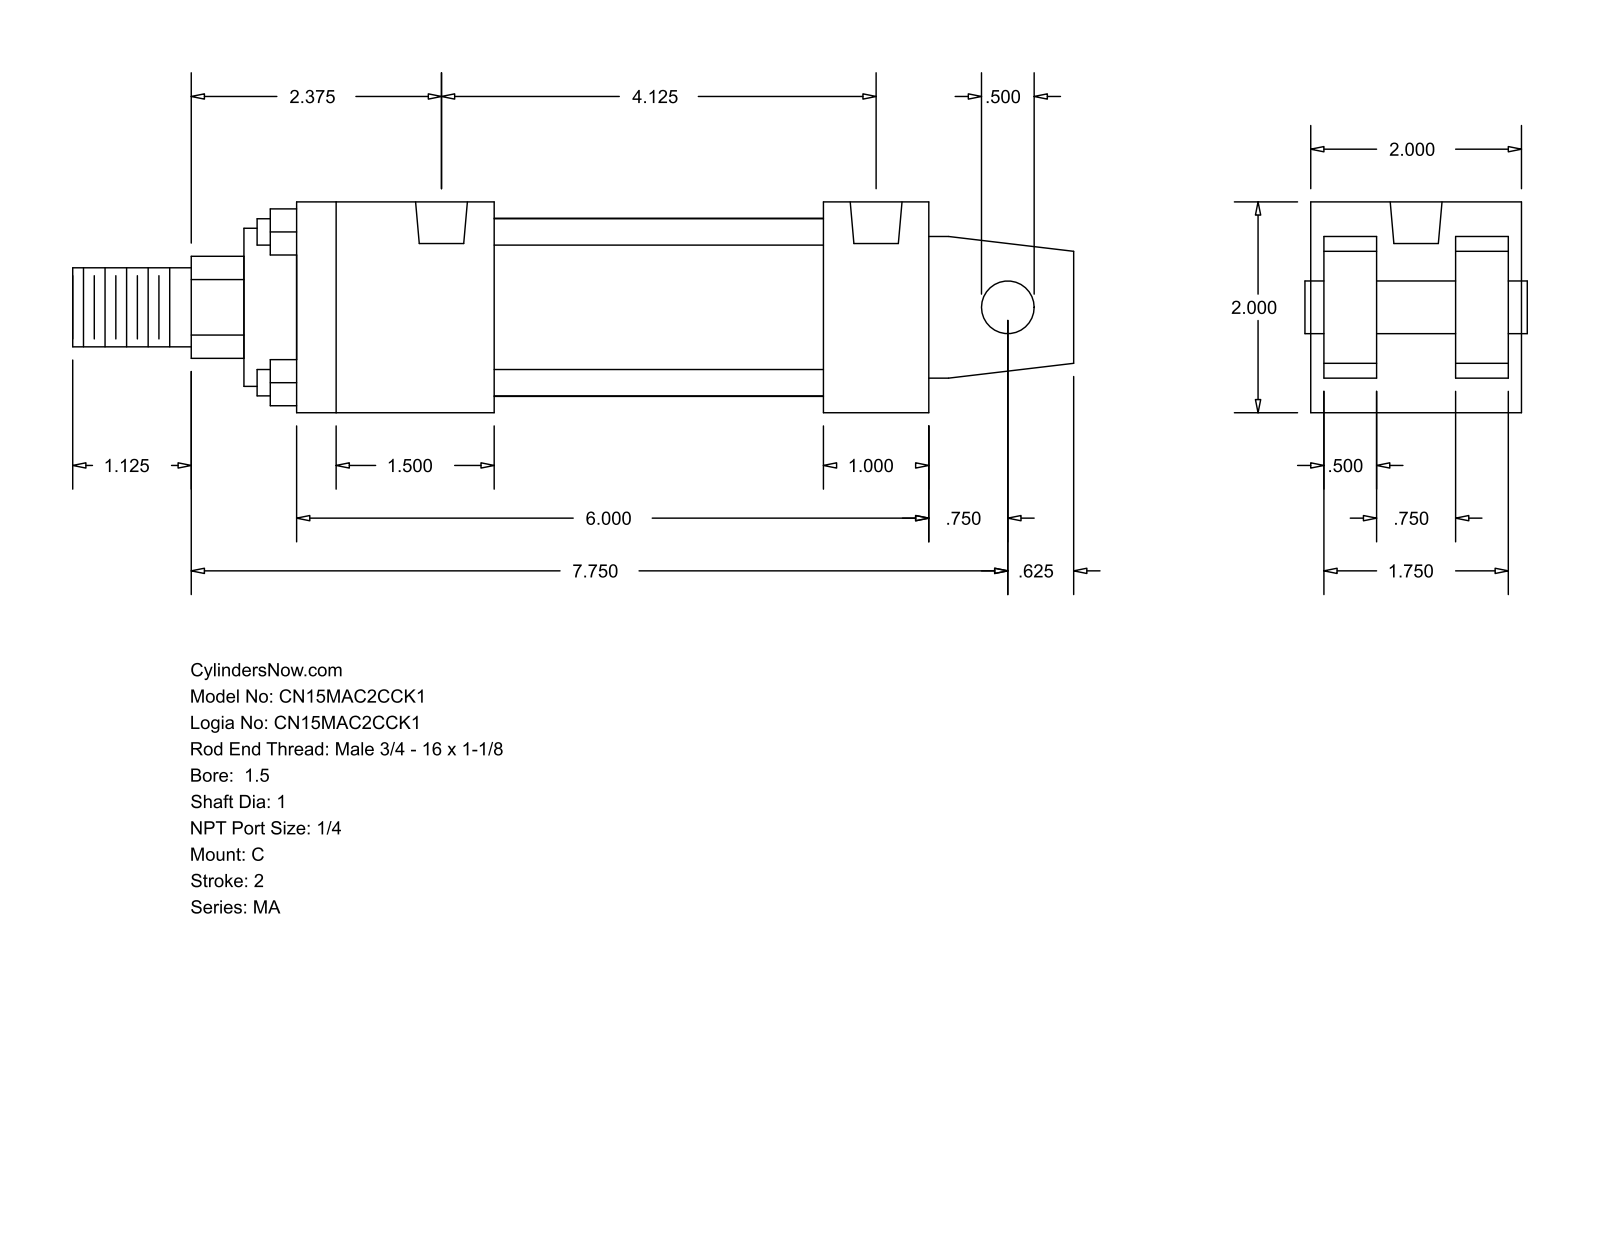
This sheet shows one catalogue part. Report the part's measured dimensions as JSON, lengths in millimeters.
{"part_name": "MA_C__0150_1", "step_written_by": "GSSL Pune (CONFIG_CONTROL_DESIGN)", "units": "millimeters", "bodies": {"solids": 0, "faces": 103, "planar": 76, "cylindrical": 27, "other": 0}, "overall_size": [241.3, 50.8, 50.8], "round_holes": [[7.94, 4], [12.49, 2]], "round_bosses_or_shafts": [[6.35, 4], [42.93, 1], [38.1, 1], [25.4, 1], [19.05, 1], [12.7, 1]], "partial_cylinders_radius": [[12.29, 1]], "face_to_face_distances": [50.8, 47.63, 12.7, 3.17, 15.87, 34.93, 31.76, 152.4, 25.4, 127], "hole_center_spacings": [104.77]}
